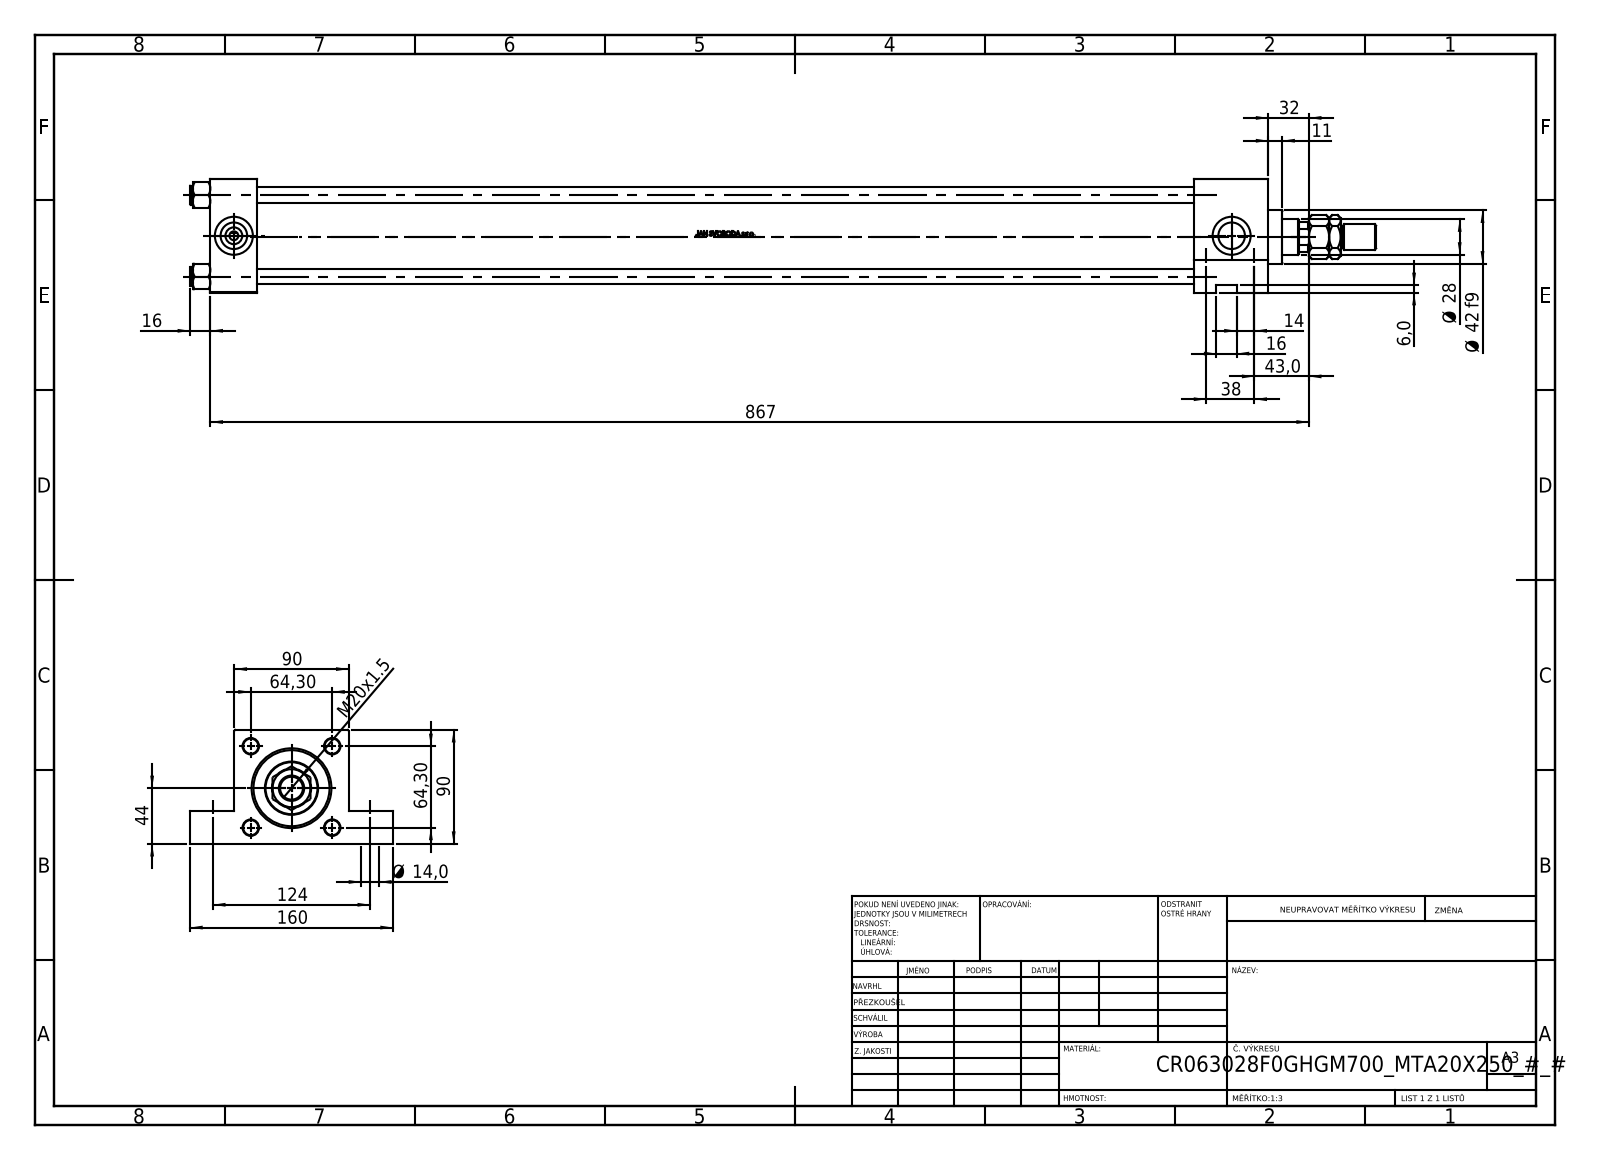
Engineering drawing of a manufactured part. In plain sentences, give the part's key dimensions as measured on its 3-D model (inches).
The part is named "V215CR_F_Body; MTA; NUT_M5_F; V215CR_VCP_F (+2 more)". Its 3-D file was written by "SolidWorks 2019 (CONFIG_CONTROL_DESIGN)". It is 12 solids with 1152 faces: 452 planar, 130 cylindrical and 570 other. Overall it measures 36.85 by 6.299 by 3.543 inches. Its volume is 134.7 cubic inches and its surface area 998.2 square inches. Round holes: 4 of diameter 0.472, 4 of diameter 0.551, 2 of diameter 0.276, 2 of diameter 0.825, 2 of diameter 1.181, 1 of diameter 0.728, 1 of diameter 1.102, 1 of diameter 1.22, 1 of diameter 1.969, 1 of diameter 2.362, 1 of diameter 2.48. Round bosses or shafts: 4 of diameter 0.591, 1 of diameter 2.717, 1 of diameter 1.654, 1 of diameter 0.787, 1 of diameter 0.709. Partial cylindrical surfaces (rounded edges, fillets, slot ends): 1 of radius 0.531. The main face-to-face distances are 3.543, 1.457, 32.874, 31.417, 30.551, 29.094, 2.323, 1.024, 2.52, 31.744. The hole center spacings are 2.531, 1.496, 1.763, 1.818, 3.58, 4.882, 5.106, 31.004.
